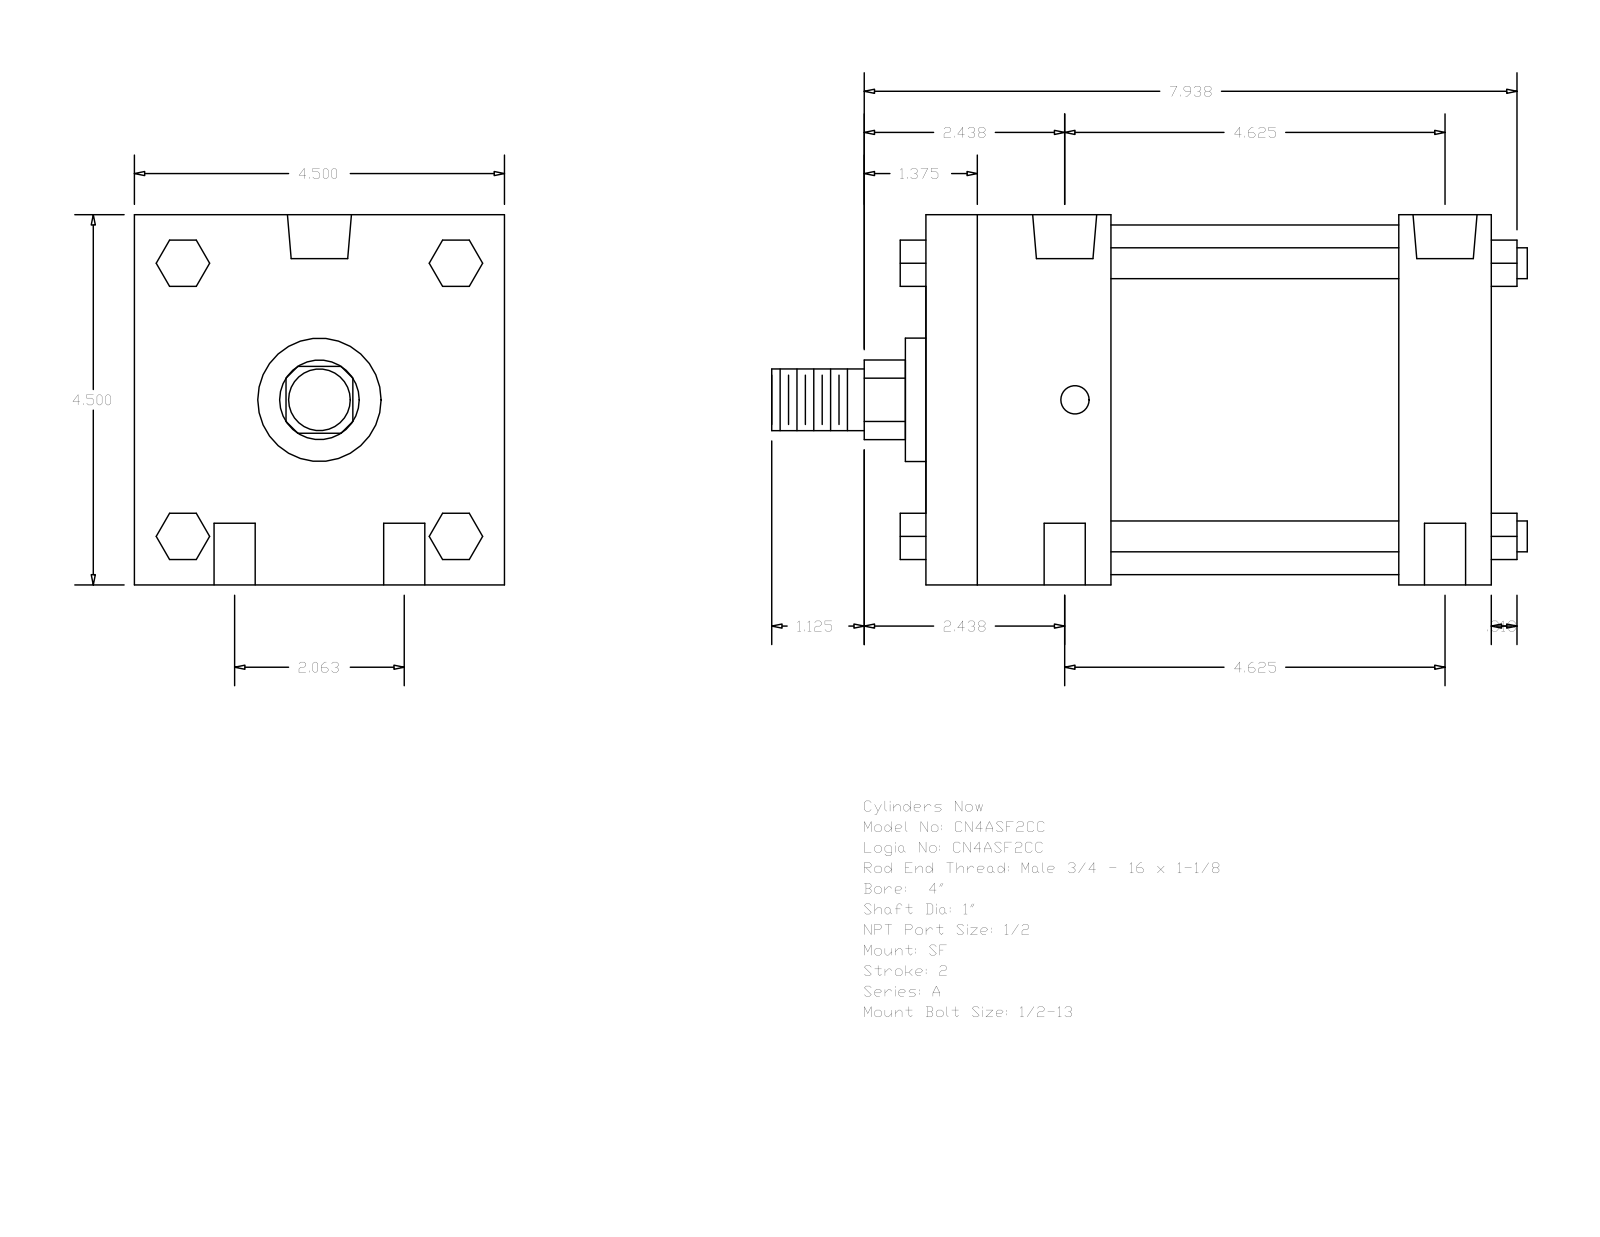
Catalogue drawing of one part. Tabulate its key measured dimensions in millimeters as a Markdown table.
| quantity | value |
| --- | --- |
| part name | A_SF__0400_1 |
| STEP written by | GSSL Pune (CONFIG_CONTROL_DESIGN) |
| units | millimeters |
| bodies | 0 solids, 124 faces (94 planar, 30 cylindrical, 0 other) |
| overall size | 233.36 × 114.3 × 114.3 |
| round holes (diameter × count) | 12.7 × 4, 8.73 × 2, 19.77 × 2 |
| round bosses / shafts (diameter × count) | 9.53 × 4, 107.95 × 1, 38.1 × 1, 25.4 × 1, 19.05 × 1 |
| partial cylindrical surfaces (radius × count) | 12.29 × 1 |
| main face-to-face distances | 114.3, 174.63, 146.05, 28.58, 57.15, 88.9, 117.48, 14.29, 42.16, 73.03 |
| hole center spacings | 26.19, 120.36, 117.48, 52.38, 128.63, 111.12 |
